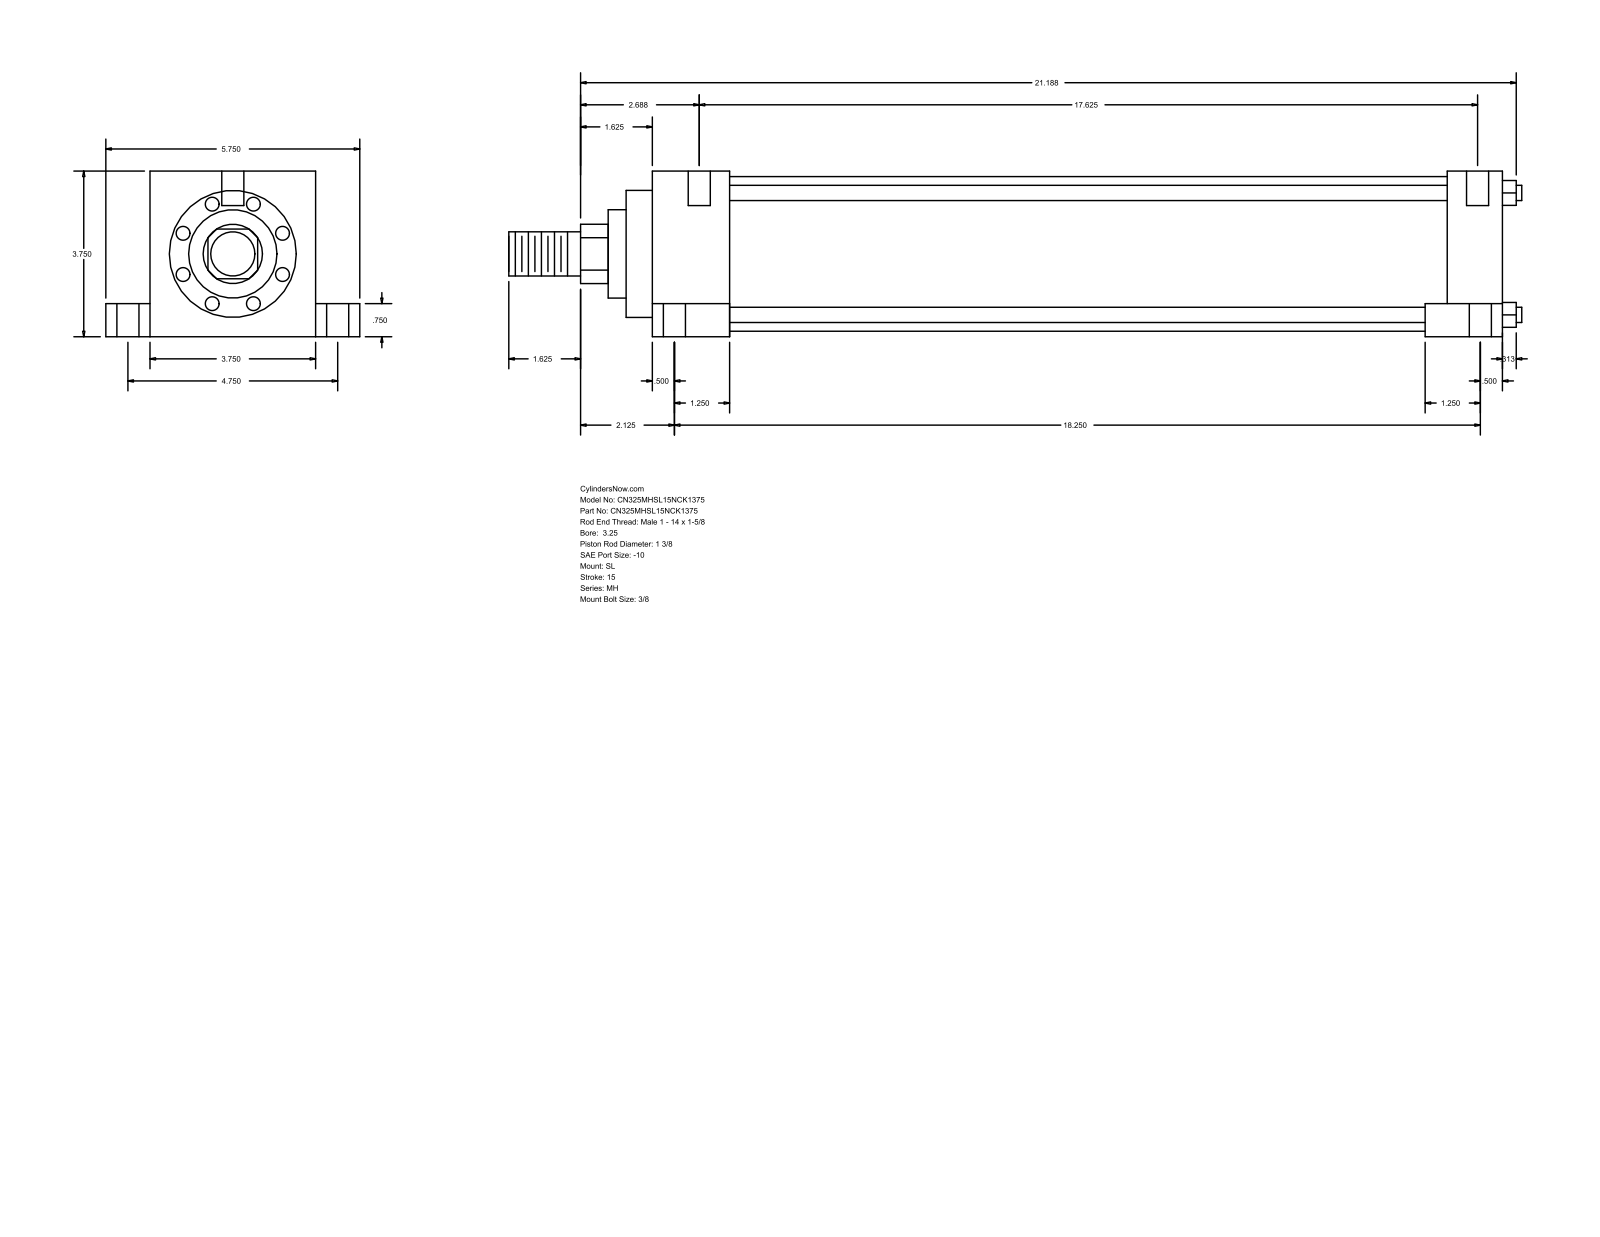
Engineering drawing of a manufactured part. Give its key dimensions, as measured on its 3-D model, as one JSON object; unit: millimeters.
{"part_name": "MH_SL__0325_1.375", "step_written_by": "GSSL Pune (CONFIG_CONTROL_DESIGN)", "units": "millimeters", "bodies": {"solids": 0, "faces": 110, "planar": 77, "cylindrical": 33, "other": 0}, "overall_size": [582.61, 146.05, 95.25], "round_holes": [[12.7, 6], [5.56, 4], [19.05, 4]], "round_bosses_or_shafts": [[8.76, 4], [88.9, 1], [73.03, 1], [50.8, 1], [34.92, 1], [25.4, 1]], "partial_cylinders_radius": [[17.06, 1]], "face_to_face_distances": [95.24, 488.96, 44.45, 444.51, 25.41, 120.65, 19.05, 76.19, 457.21, 412.76], "hole_center_spacings": [60.35, 60.41, 61.65, 62, 120.66, 453.29, 454.03, 454.87]}
